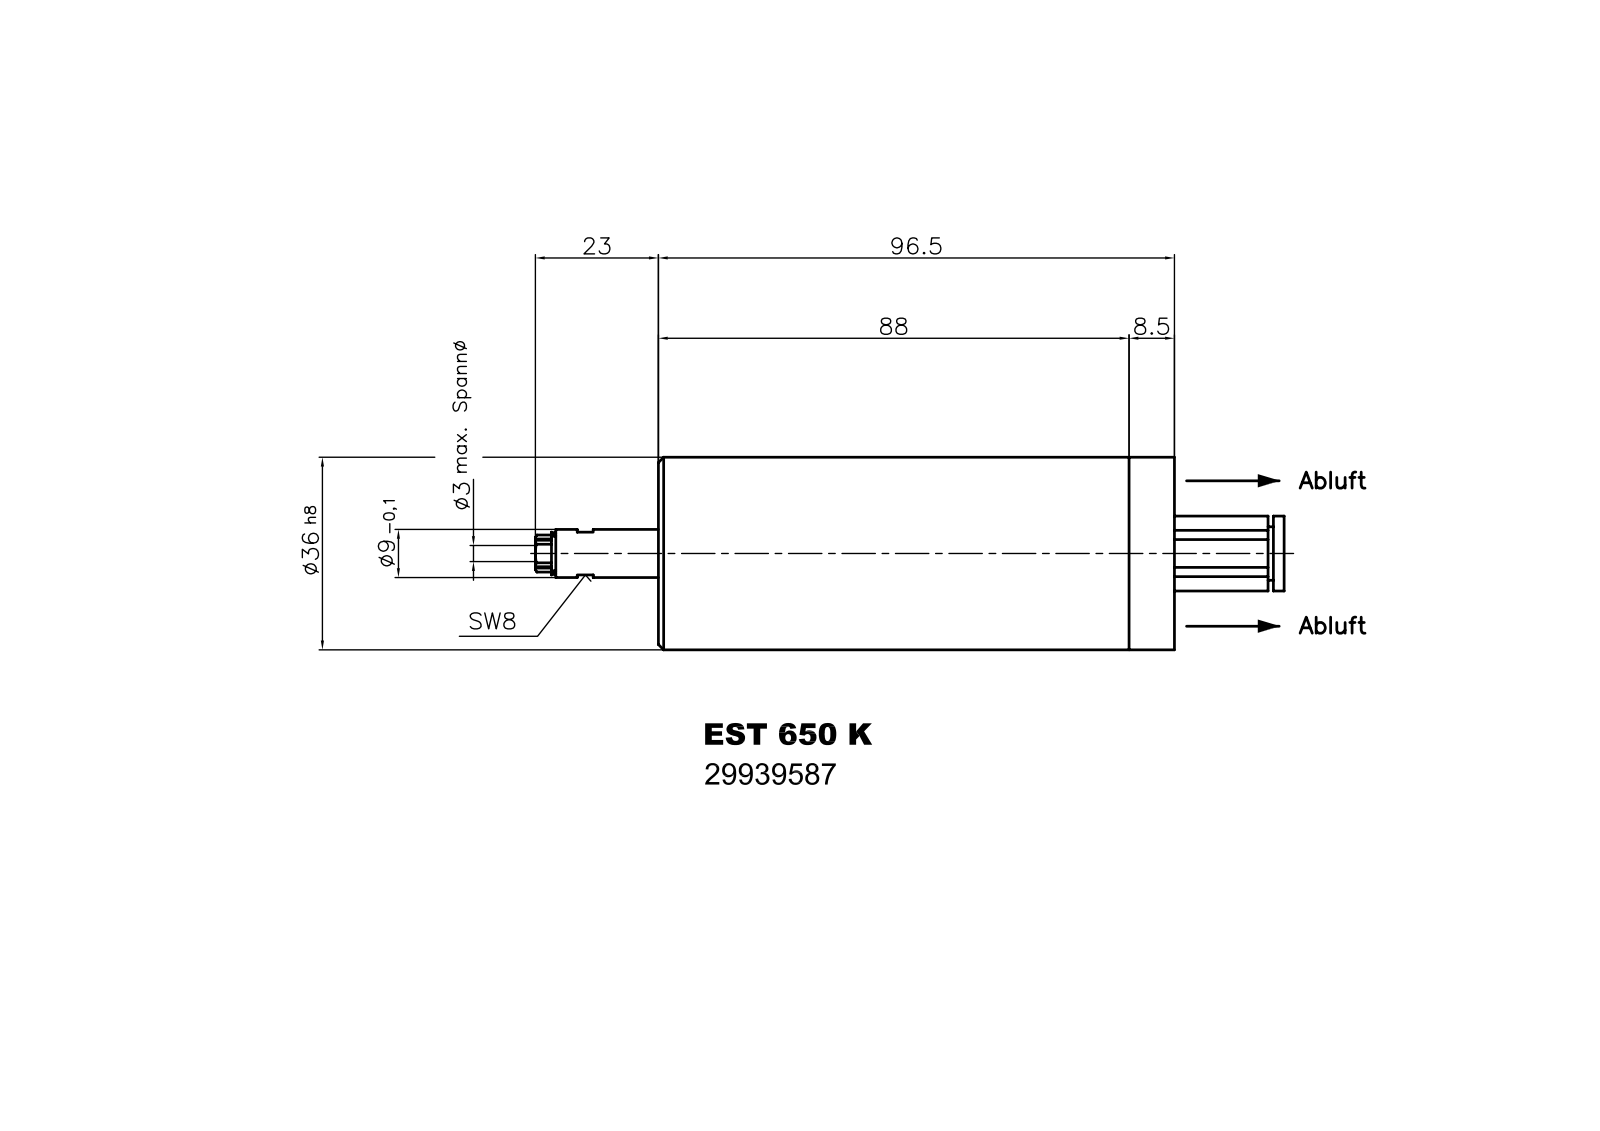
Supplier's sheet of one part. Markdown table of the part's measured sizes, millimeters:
| quantity | value |
| --- | --- |
| part name | Bauteil14 |
| STEP written by | Autodesk Inventor 2008 (AUTOMOTIVE_DESIGN) |
| units | millimeters |
| bodies | 1 solid, 137 faces (69 planar, 30 cylindrical, 38 other) |
| overall size | 140.18 × 36 × 36 |
| volume | 101 159 mm³ |
| surface area | 15 739 mm² |
| round holes (diameter × count) | 3 × 1, 3.1 × 1, 8 × 1, 9.5 × 1, 12.1 × 1 |
| round bosses / shafts (diameter × count) | 36 × 1, 13 × 1, 12 × 1, 9.2 × 1, 9 × 1, 8.57 × 1 |
| partial cylindrical surfaces (radius × count) | 5 × 3, 2.5 × 1, 6.75 × 1, 7.25 × 1 |
| main face-to-face distances | 96.5, 7, 6.5, 13.5, 13, 114.5, 18, 117.2, 20.7, 2.7 |
